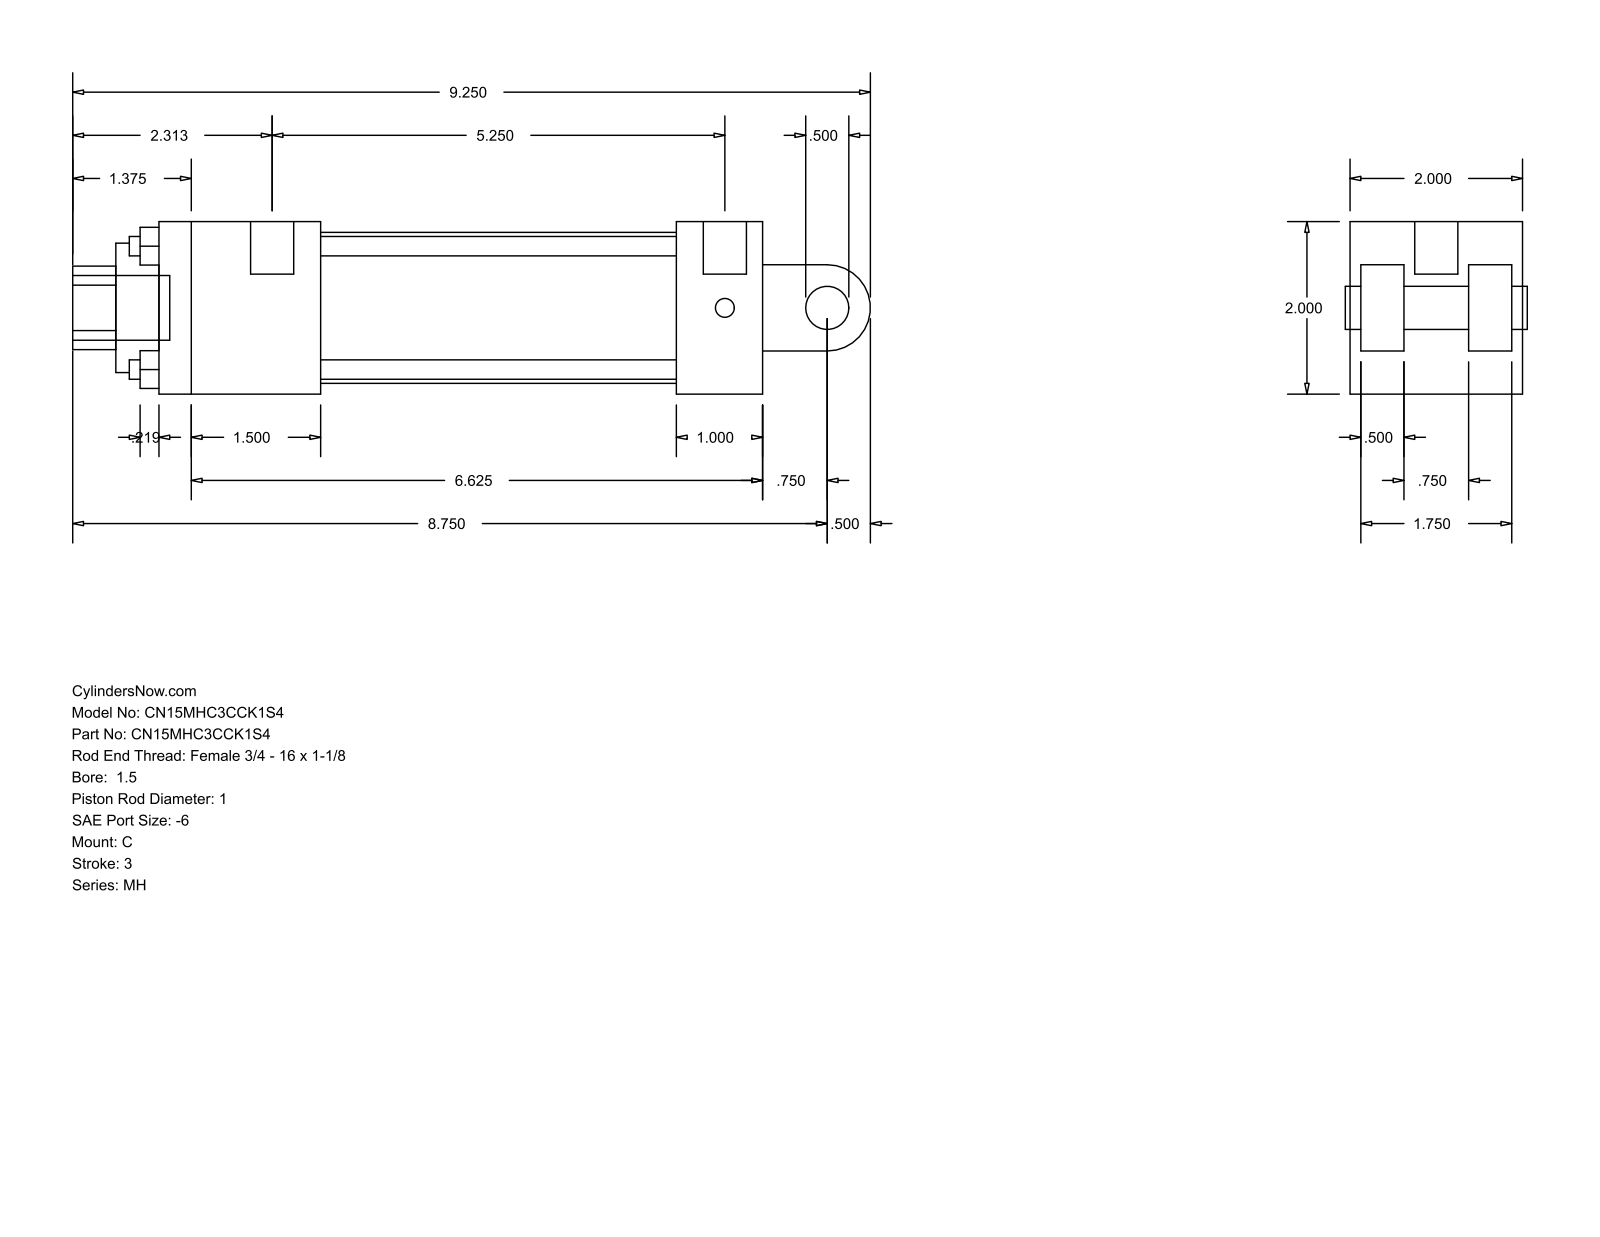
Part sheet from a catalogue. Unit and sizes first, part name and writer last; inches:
Units: inches
Overall size (bounding box): 9.25 × 2 × 2
Round holes (diameter × count): ⌀0.225 ×4, ⌀0.219 ×2, ⌀0.5 ×1, ⌀1 ×1, ⌀1.5 ×1, ⌀1.75 ×1
Round bosses / shafts (diameter × count): ⌀0.5 ×2, ⌀0.219 ×2, ⌀0.75 ×1
Partial cylindrical surfaces — rounded edges, fillets, slot ends (radius × count): R0.484 ×1, R0.5 ×1
Main face-to-face distances: 2, 0.5, 1.875, 0.125, 0.625, 1, 1.375, 1.25, 7, 1.5
Hole centre spacings: 1.011, 1.43, 2.022
Bodies: 0 solids, 99 faces (70 planar, 29 cylindrical, 0 other)
Part name (STEP PRODUCT): MH_C__0150_1
STEP written by: GSSL Pune (CONFIG_CONTROL_DESIGN)
